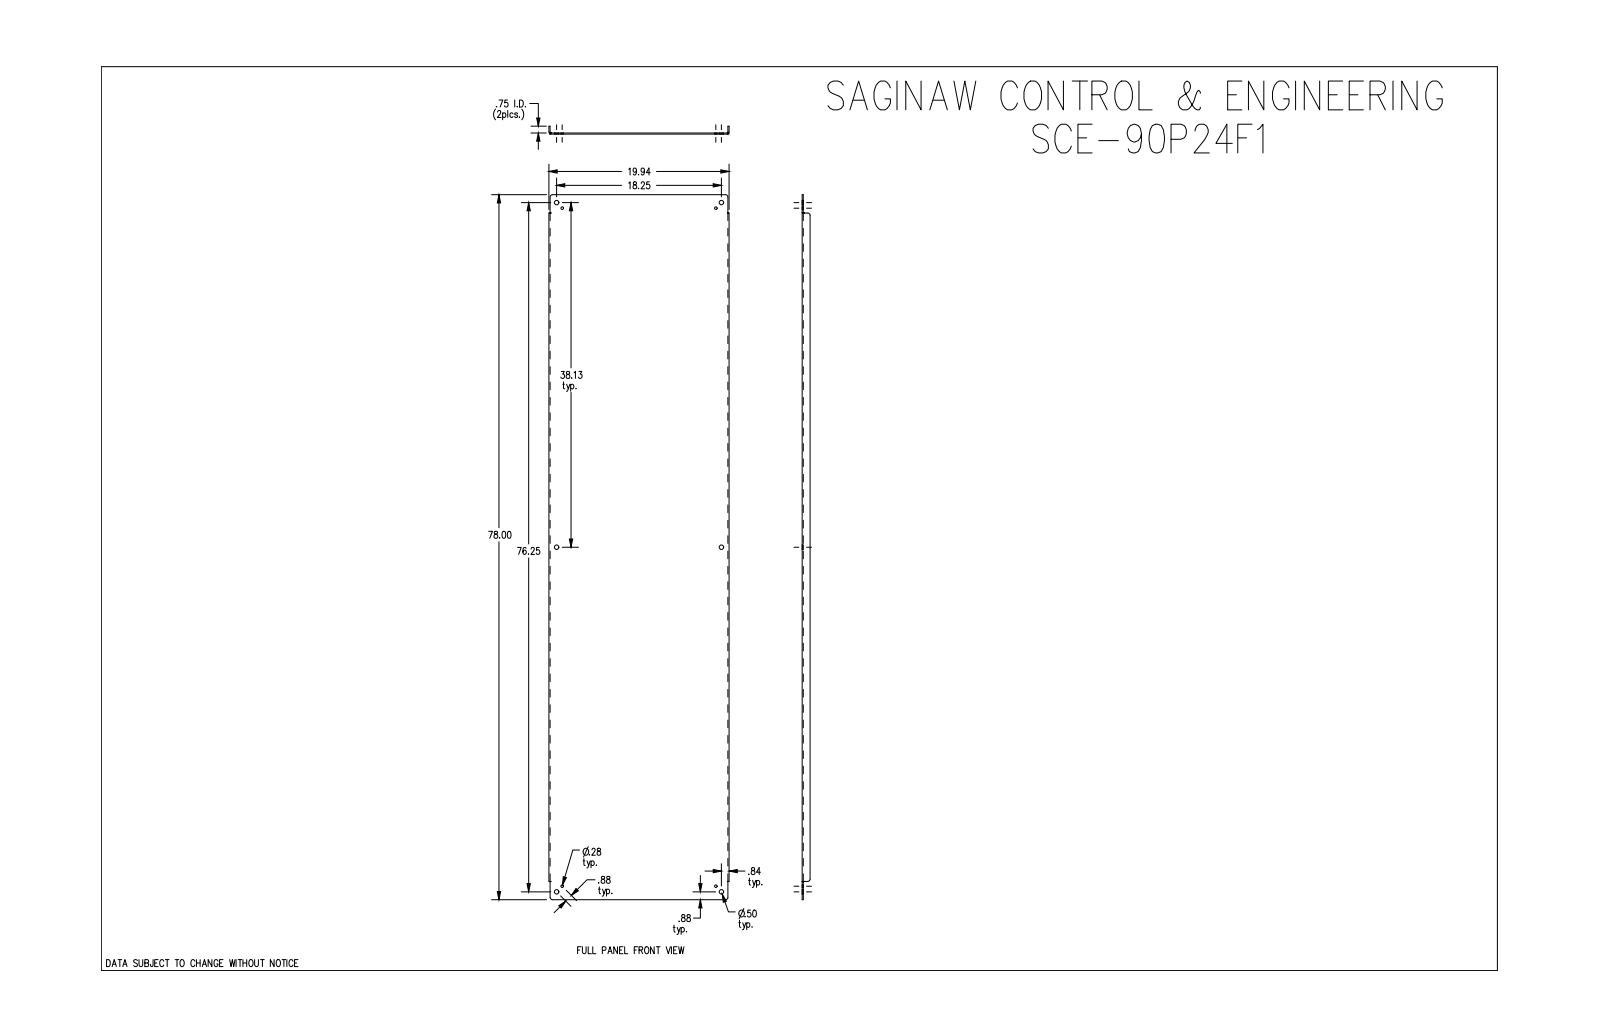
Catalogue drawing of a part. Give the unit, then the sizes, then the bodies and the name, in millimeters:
Units: millimetres
Overall size (bounding box): 1981.2 × 506.4 × 22.2
Round holes (diameter × count): ⌀12.7 ×6, ⌀7.1 ×4
Partial cylindrical surfaces — rounded edges, fillets, slot ends (radius × count): R6.4 ×6, R2.8 ×2, R6 ×2
Main face-to-face distances: 3.2, 3.2, 503.3, 500, 506.4, 19.1, 22.2, 1981.2, 51.6, 1929.6
Hole centre spacings: 22.2, 448.1, 952.8, 968.4, 1052.7, 1073.6, 1921.1, 1972.5
Volume: 3 386 000 mm³ · Surface area: 2 149 000 mm²
Bodies: 1 solid, 52 faces (18 planar, 22 cylindrical, 12 other)
Part name (STEP PRODUCT): SCE-90P24F1
STEP written by: SolidWorks 2019 (AUTOMOTIVE_DESIGN)
